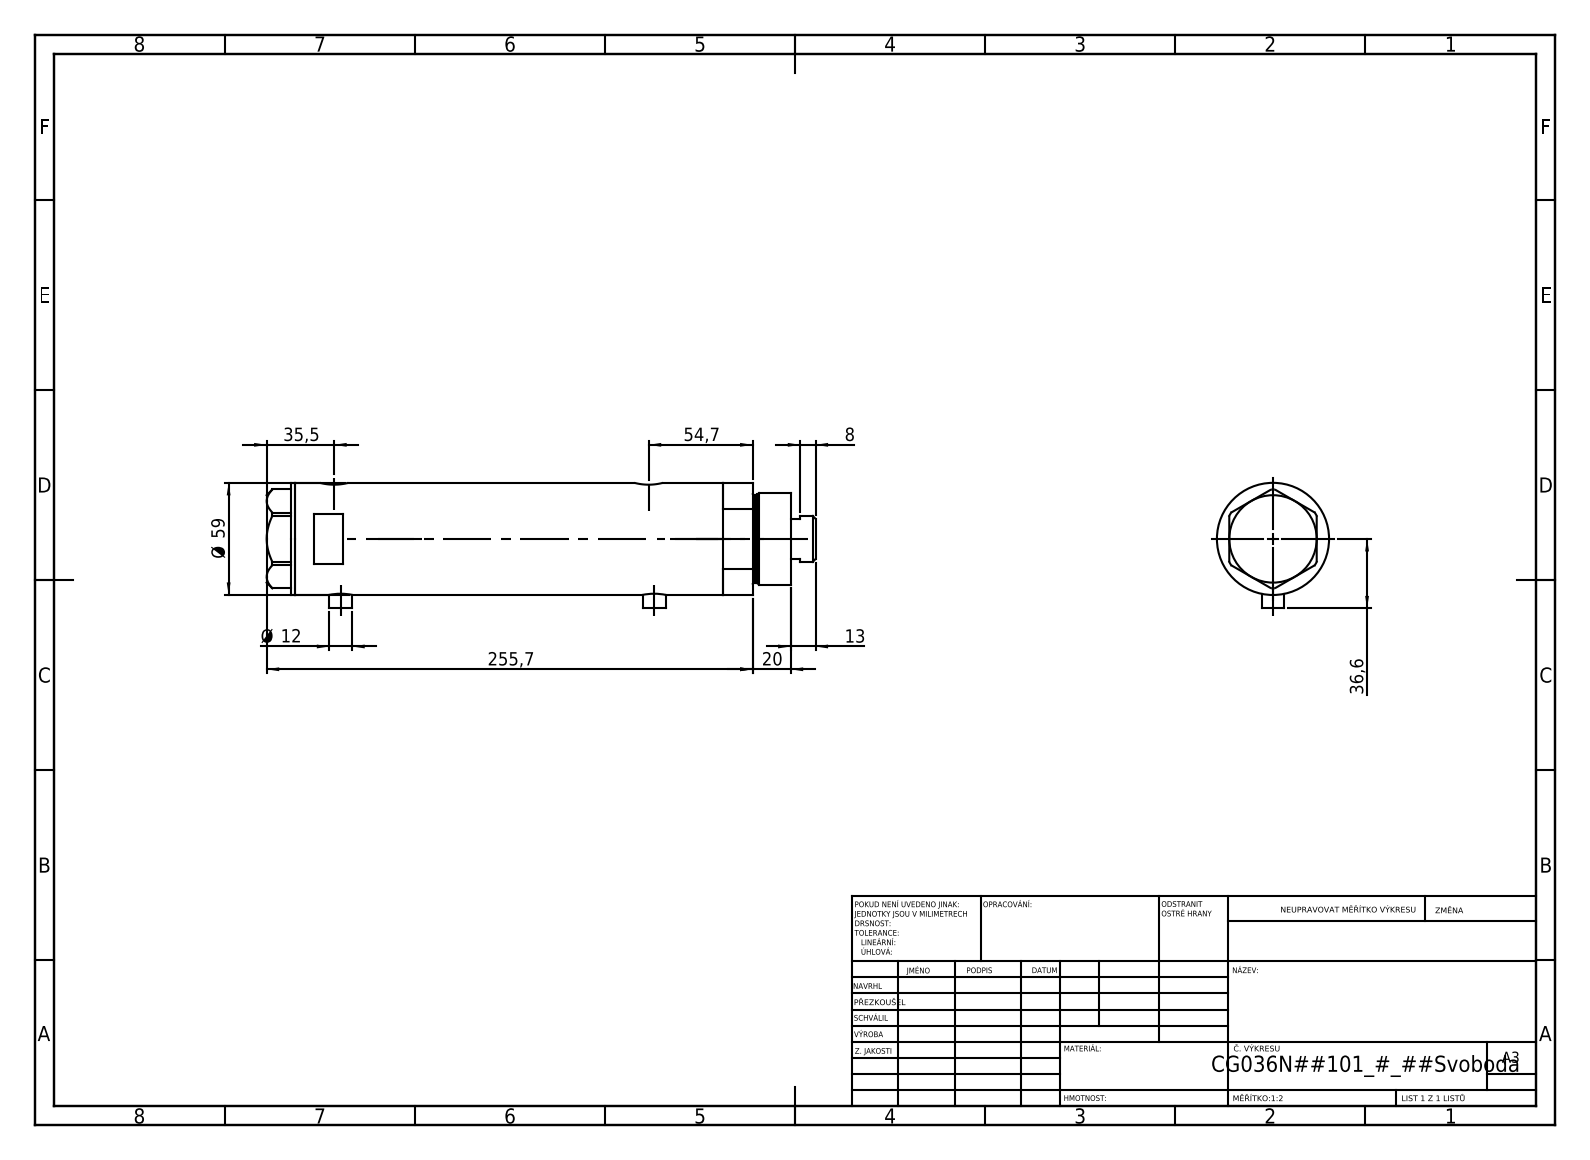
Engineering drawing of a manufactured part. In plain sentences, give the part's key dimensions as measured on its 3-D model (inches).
The part is named "V270CG_FRONT; V270CG_VC; V270CG_MIDDLE; V270CG_BACK". Its 3-D file was written by "SolidWorks 2019 (CONFIG_CONTROL_DESIGN)". It is 4 solids with 126 faces: 53 planar, 53 cylindrical and 20 other. Overall it measures 11.37 by 2.602 by 2.323 inches. Its volume is 40.73 cubic inches and its surface area 203.8 square inches. Round holes: 2 of diameter 0.197, 2 of diameter 0.383, 2 of diameter 0.492, 2 of diameter 0.591, 1 of diameter 0.335, 1 of diameter 0.984, 1 of diameter 1.043, 1 of diameter 1.417, 1 of diameter 1.575, 1 of diameter 2.047. Round bosses or shafts: 2 of diameter 0.472, 1 of diameter 2.323, 1 of diameter 1.89, 1 of diameter 1.811, 1 of diameter 0.945. The main face-to-face distances are 7.37, 0.925, 6.445, 0.591, 1.516, 7.961, 0.079, 10.264, 10.854, 9.339. The hole center spacings are 0.114, 0.138, 6.378, 6.492, 6.516, 6.63.
